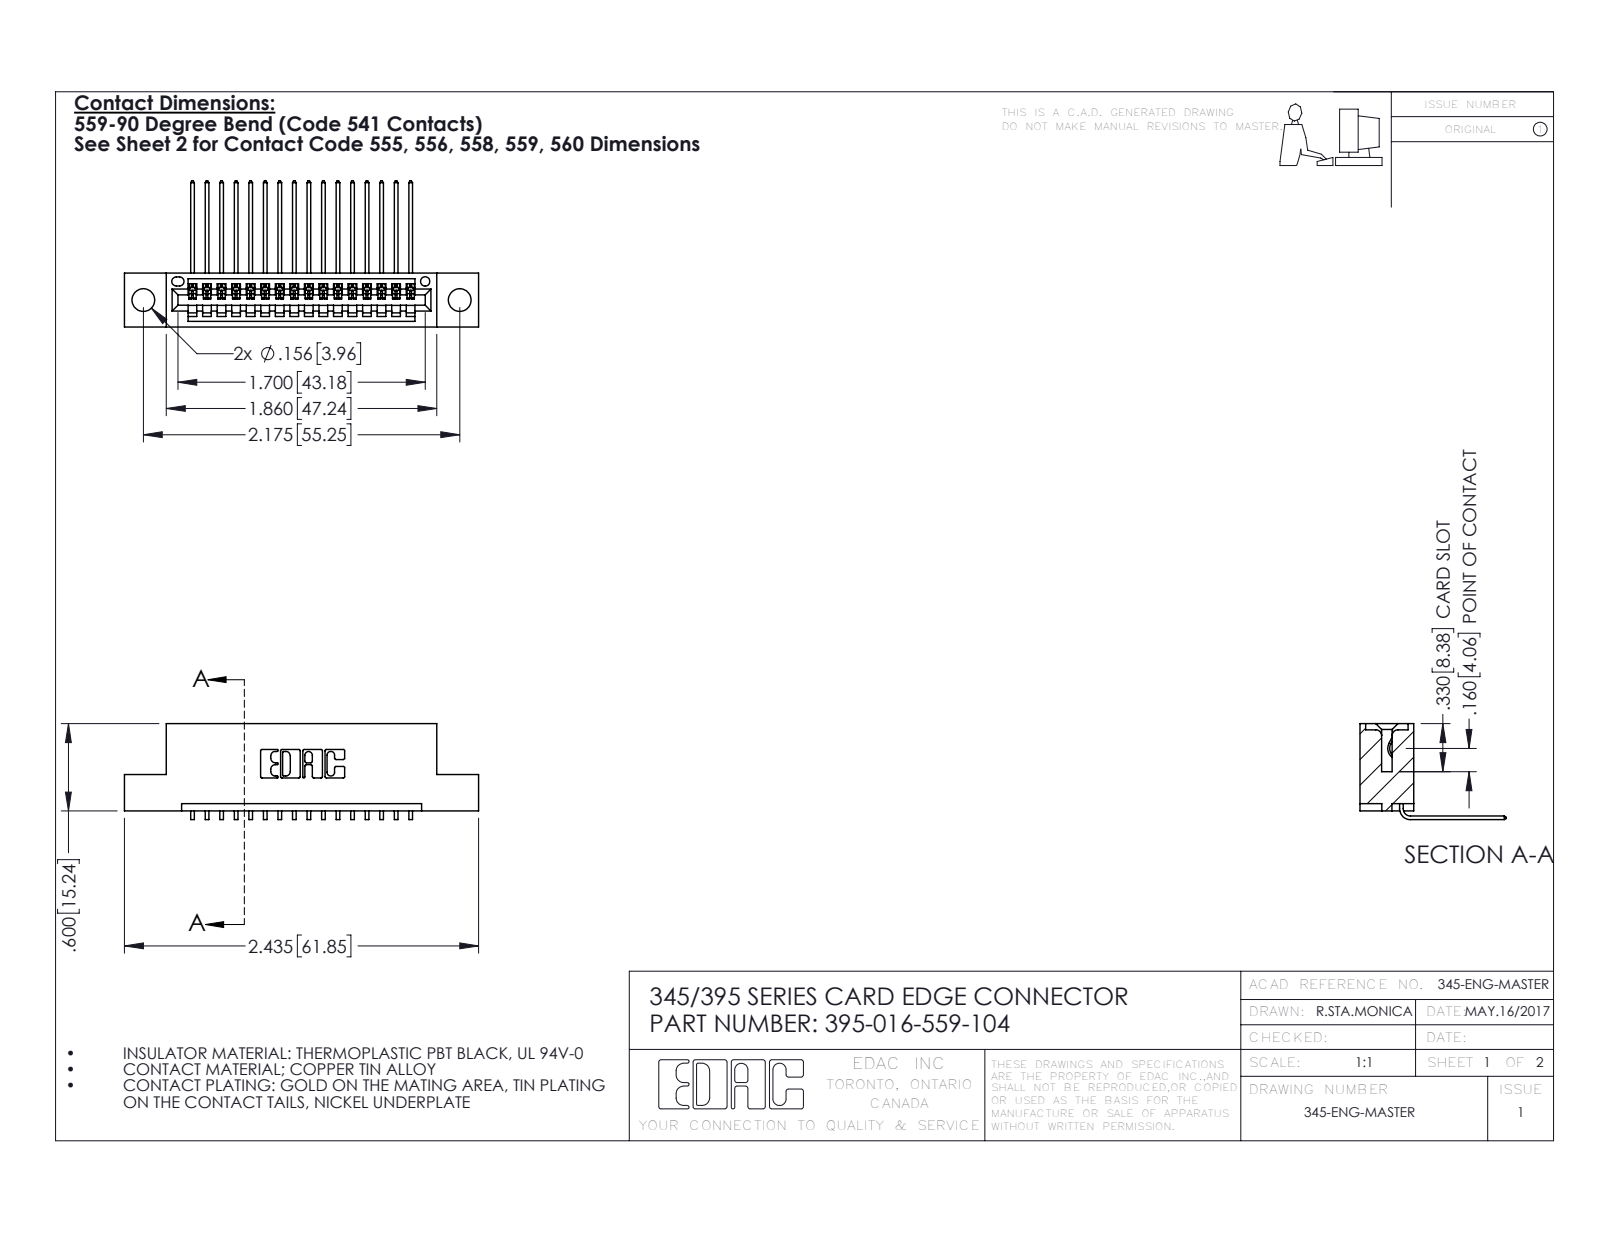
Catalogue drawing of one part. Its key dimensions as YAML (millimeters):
part_name: "345-292-001_558 559 Tail - 1; 345 Part_Flush Mounting Lugs - 0.156 Dia-TH; 395-016-559-104"
step_written_by: "SolidWorks 2016 (CONFIG_CONTROL_DESIGN)"
units: millimeters
bodies: {solids: 17, faces: 1086, planar: 752, cylindrical: 334, other: 0}
overall_size: [61.8, 25.5, 16.7]
volume: 5620
surface_area: 7245
round_holes:
  - {diameter: 4, count: 2}
  - {diameter: 1.6, count: 1}
partial_cylinders:
  - {radius: 0.2, count: 32}
  - {radius: 0.3, count: 22}
  - {radius: 0.2, count: 6}
  - {radius: 0.8, count: 6}
  - {radius: 0.7, count: 3}
  - {radius: 0.8, count: 2}
  - {radius: 1, count: 2}
  - {radius: 0.4, count: 1}
face_to_face_distances: [7.6, 1.8, 5.1, 9.4, 2.5, 6.9, 0.6, 5.7, 2.5, 1.3]
hole_center_spacings: [6.9, 49.3, 55.2]
